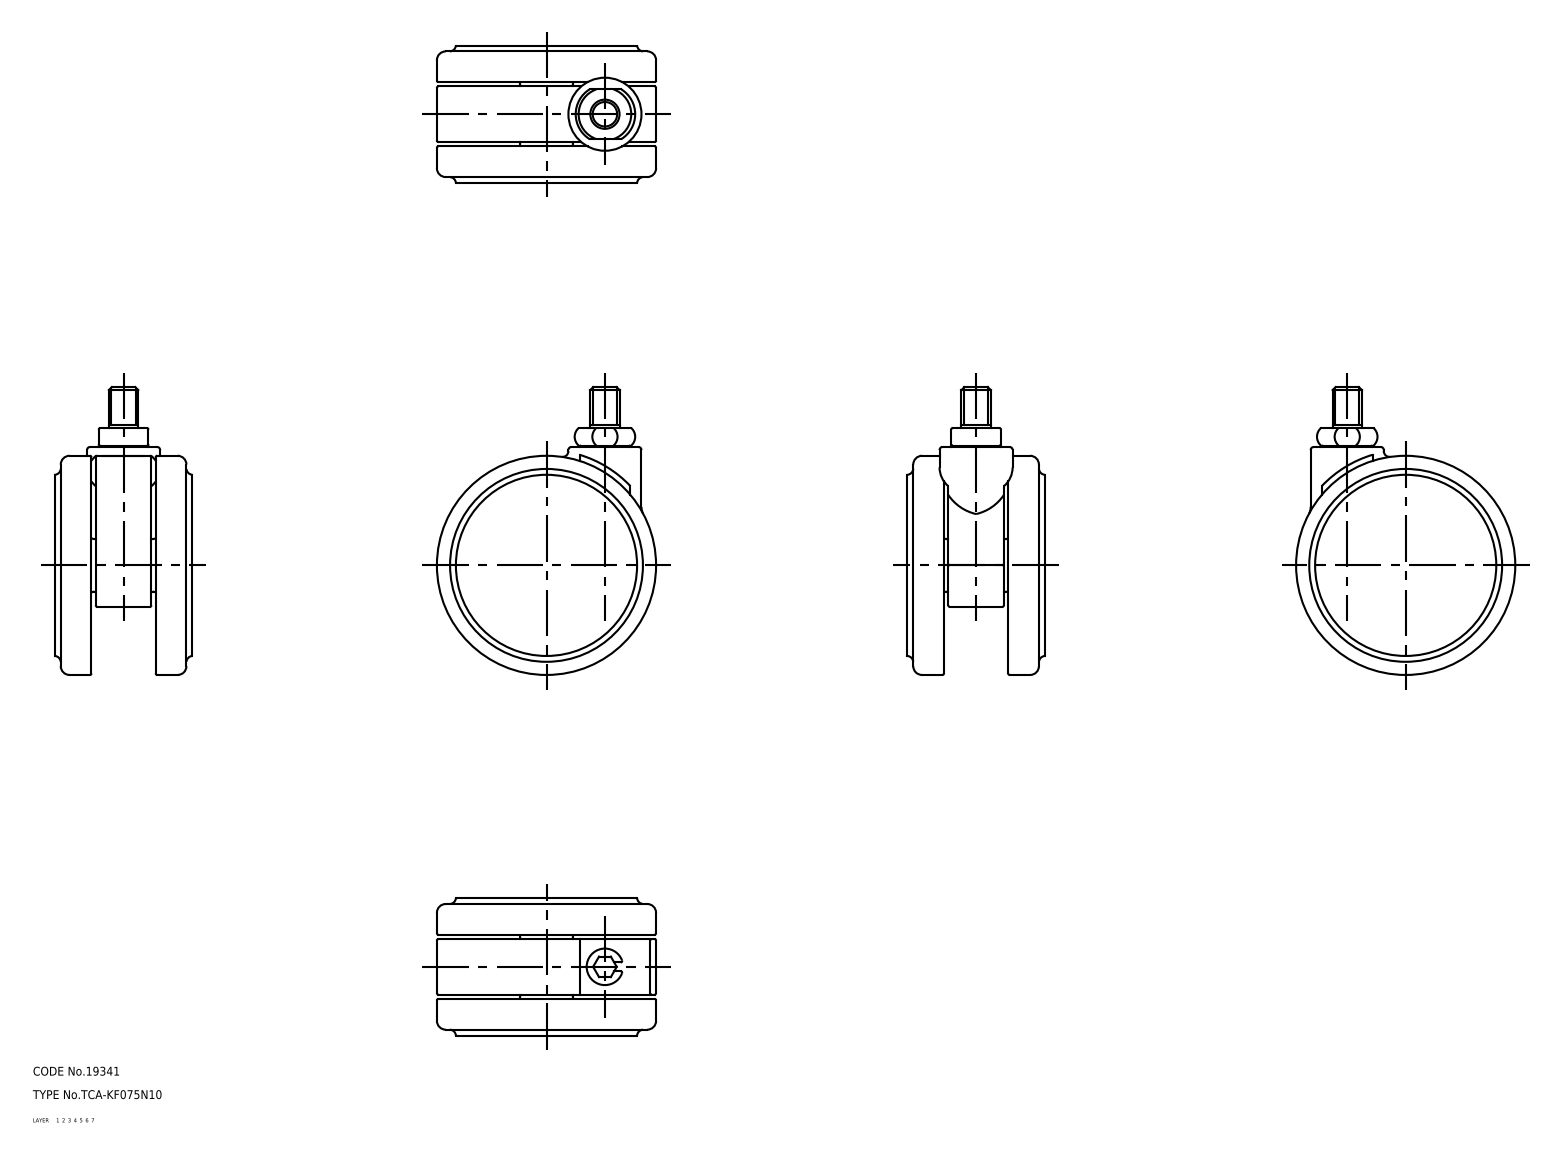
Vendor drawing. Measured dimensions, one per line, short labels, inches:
name: main shaft; wheel; wheel_mr; TCA_KF075N10
written by: SolidWorks 2015 (AUTOMOTIVE_DESIGN)
unit: in
bodies: 4 solids, 126 faces (35 planar, 45 cylindrical, 46 other)
size: 3.878 × 2.953 × 1.85
volume: 9.753 in³; area: 57.17 in²
holes: 1× ⌀0.236, 1× ⌀1.693
bosses: 1× ⌀2.953, 1× ⌀0.984, 1× ⌀0.709, 1× ⌀0.669, 1× ⌀0.492, 1× ⌀0.394
rounds: 13× R0.02, 1× R0.039, 1× R0.114, 1× R0.567, 1× R1.555
face distances: 0.551, 1.299, 0.059, 0.807, 0.492, 1.358, 1.85, 0.748, 0.866, 0.984
